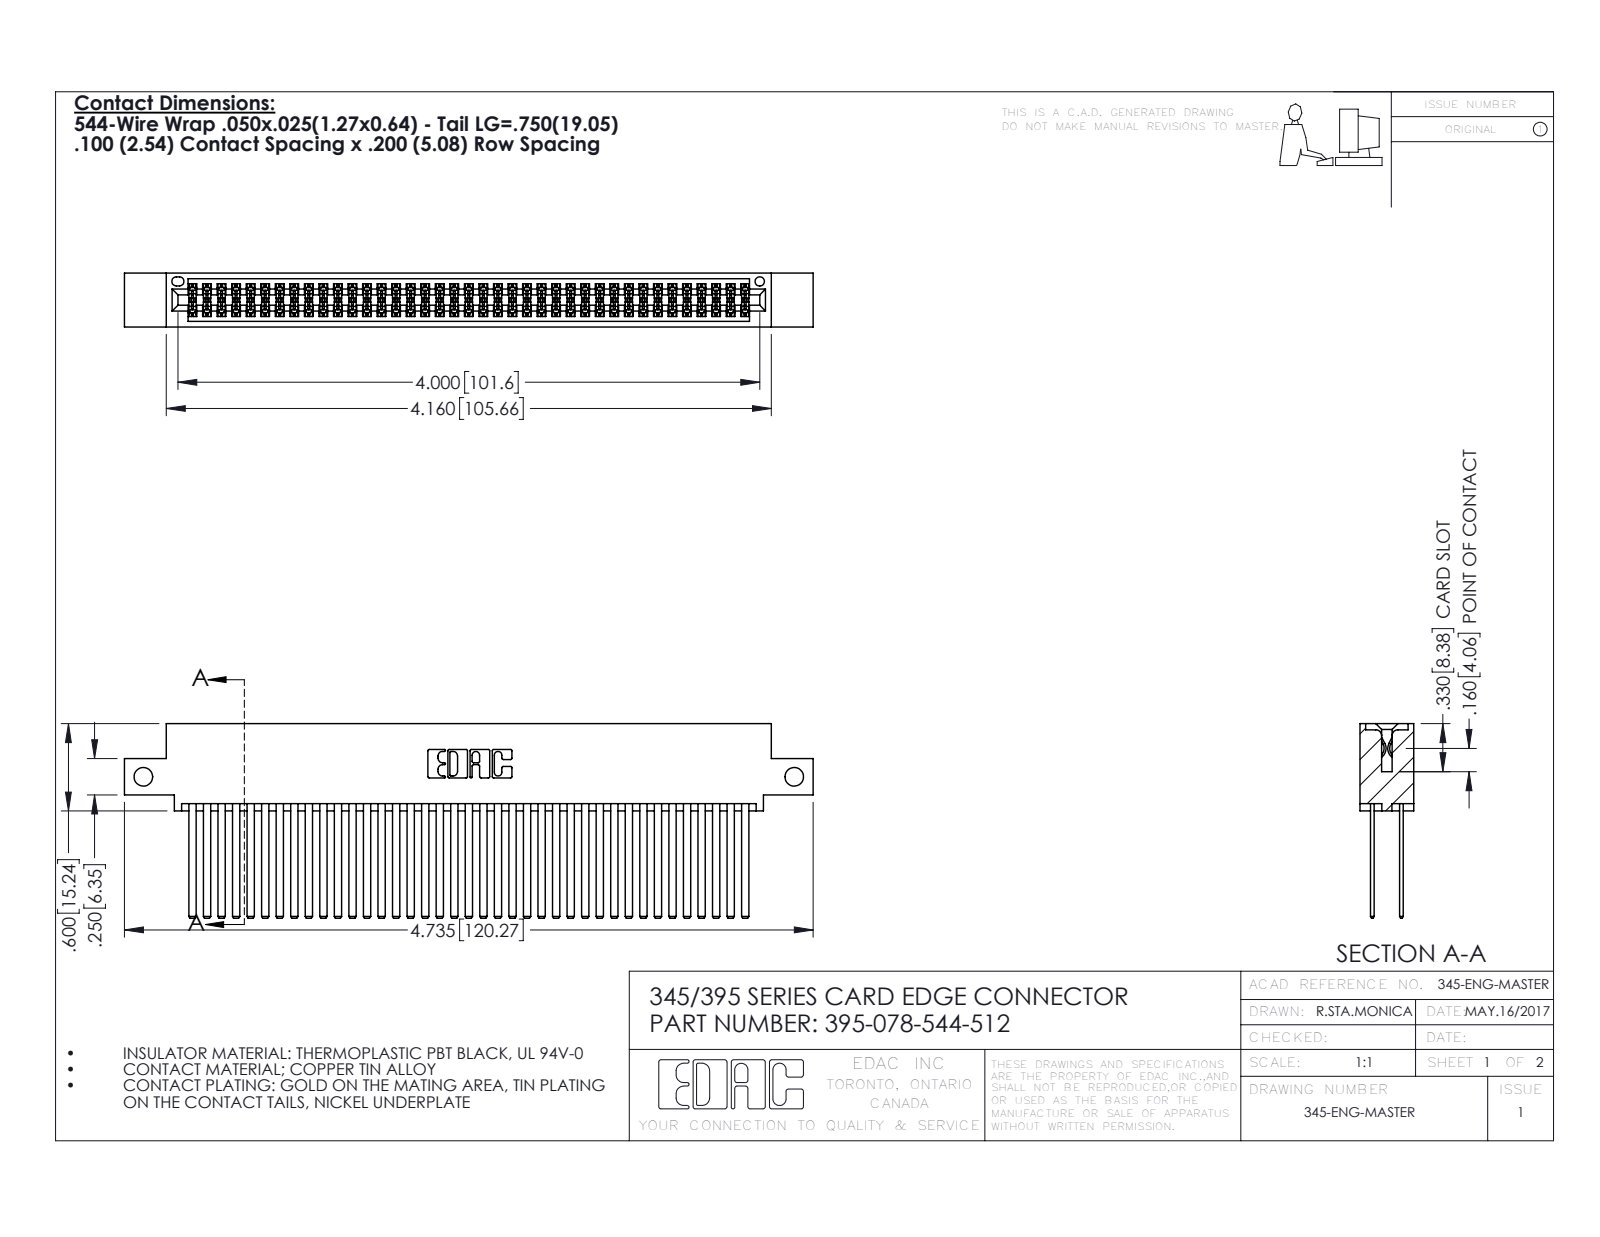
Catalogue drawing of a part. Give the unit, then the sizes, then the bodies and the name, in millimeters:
Units: millimetres
Overall size (bounding box): 120.3 × 34 × 9.4
Round holes (diameter × count): ⌀3.3 ×2, ⌀1.6 ×1
Partial cylindrical surfaces — rounded edges, fillets, slot ends (radius × count): R0.2 ×117, R0.3 ×22, R0.2 ×6, R0.8 ×6, R0.7 ×3, R0.4 ×2, R0.5 ×2, R0.6 ×2
Main face-to-face distances: 5.1, 0.6, 7.6, 1.8, 2.5, 6.9, 5.7, 4.4, 9.4, 1.3
Hole centre spacings: 113.7
Volume: 12 600 mm³ · Surface area: 21 710 mm²
Bodies: 79 solids, 3562 faces (2346 planar, 1216 cylindrical, 0 other)
Part name (STEP PRODUCT): 345-292-001_345-293-144; 395-078-544-512; 345 Part_0.110 Offset - Side Mount
STEP written by: SolidWorks 2016 (CONFIG_CONTROL_DESIGN)
